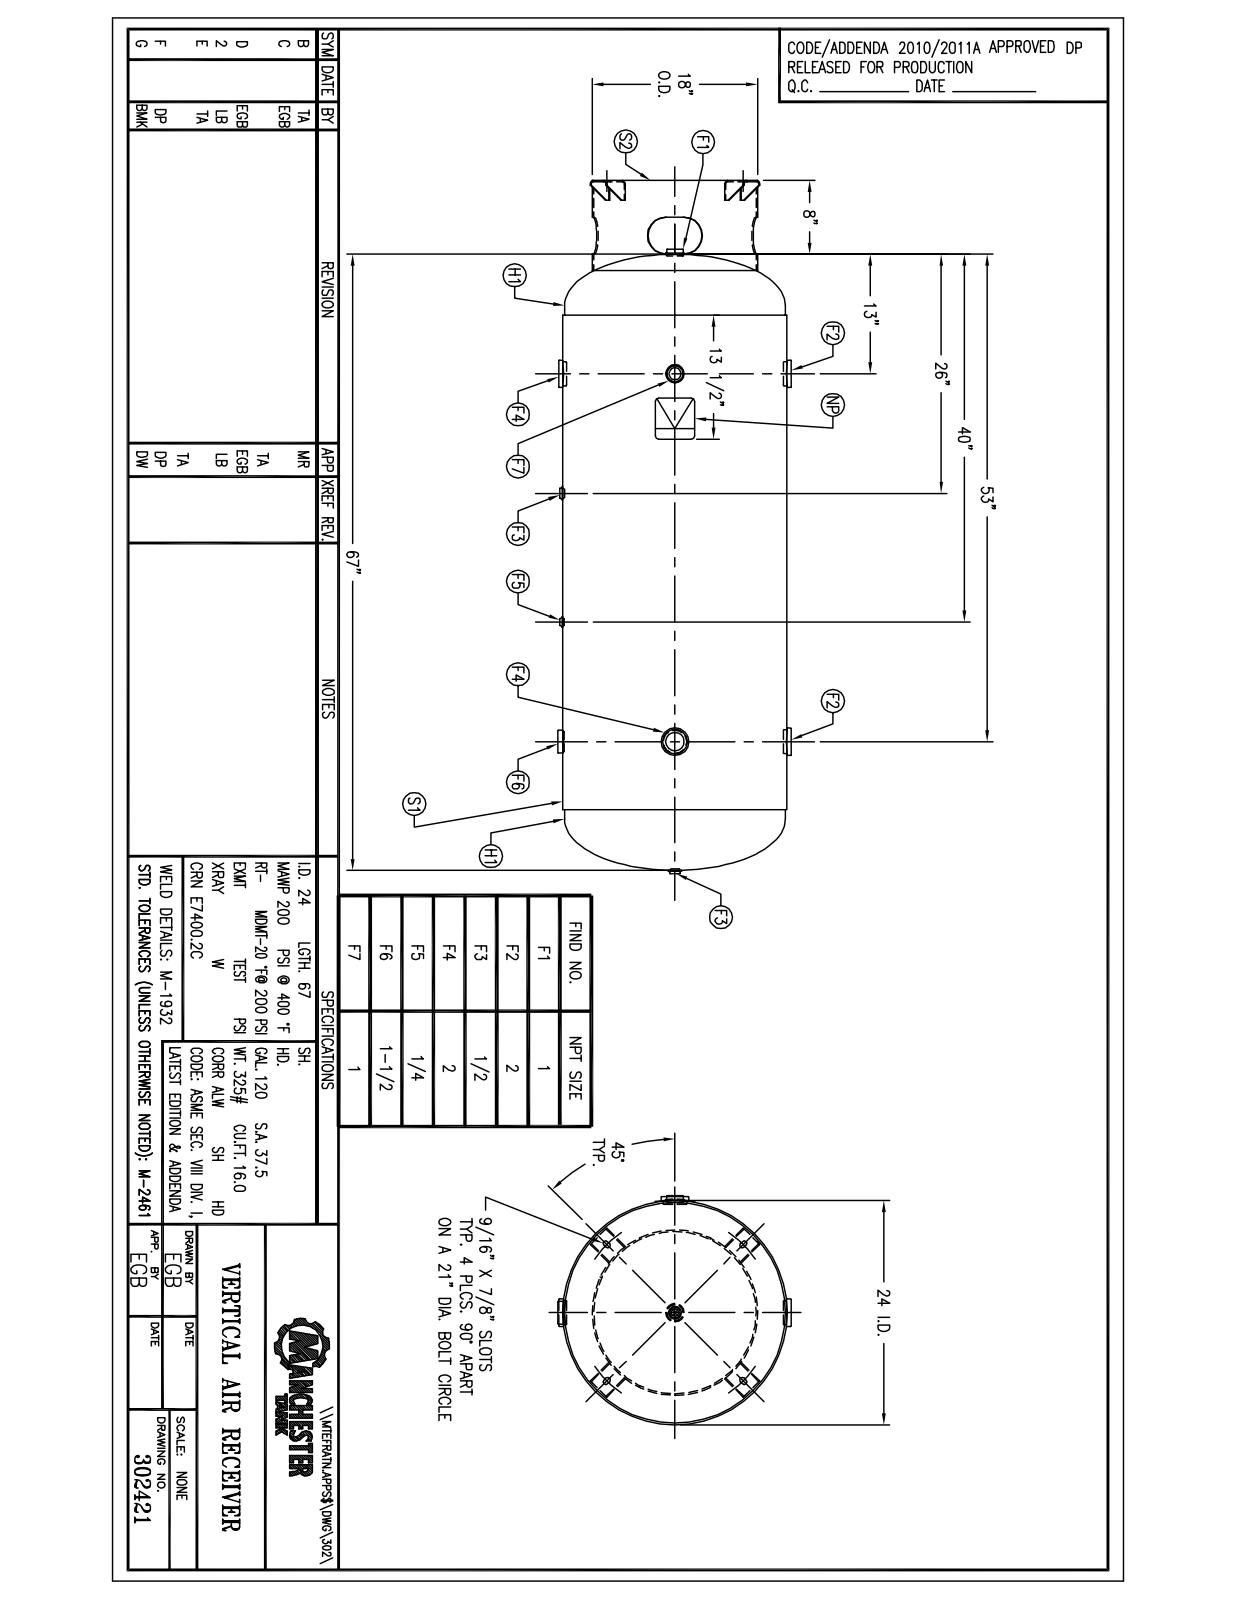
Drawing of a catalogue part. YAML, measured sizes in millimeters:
part_name: "302421"
step_written_by: "SolidWorks 2011 (CONFIG_CONTROL_DESIGN)"
units: millimeters
bodies: {solids: 0, faces: 276, planar: 95, cylindrical: 89, other: 92}
overall_size: [1910.4, 657, 640.3]
round_holes:
  - {diameter: 60.3, count: 3}
  - {diameter: 21.3, count: 2}
  - {diameter: 13.7, count: 1}
  - {diameter: 33.4, count: 1}
  - {diameter: 48.3, count: 1}
  - {diameter: 447.7, count: 1}
round_bosses_or_shafts:
  - {diameter: 36.8, count: 3}
  - {diameter: 36.5, count: 3}
  - {diameter: 76.2, count: 2}
  - {diameter: 66.7, count: 2}
  - {diameter: 618.9, count: 1}
  - {diameter: 609.6, count: 1}
  - {diameter: 457.2, count: 1}
  - {diameter: 92.1, count: 1}
partial_cylinders:
  - {radius: 6.4, count: 8}
  - {radius: 7.1, count: 8}
  - {radius: 9.8, count: 8}
  - {radius: 306.3, count: 1}
face_to_face_distances: [3.4, 1.6, 62.1, 1731.6, 1735, 1365.3, 366.4, 369.8, 65.5, 63.7]
hole_center_spacings: [330.2, 685.8, 1016, 355.6]
